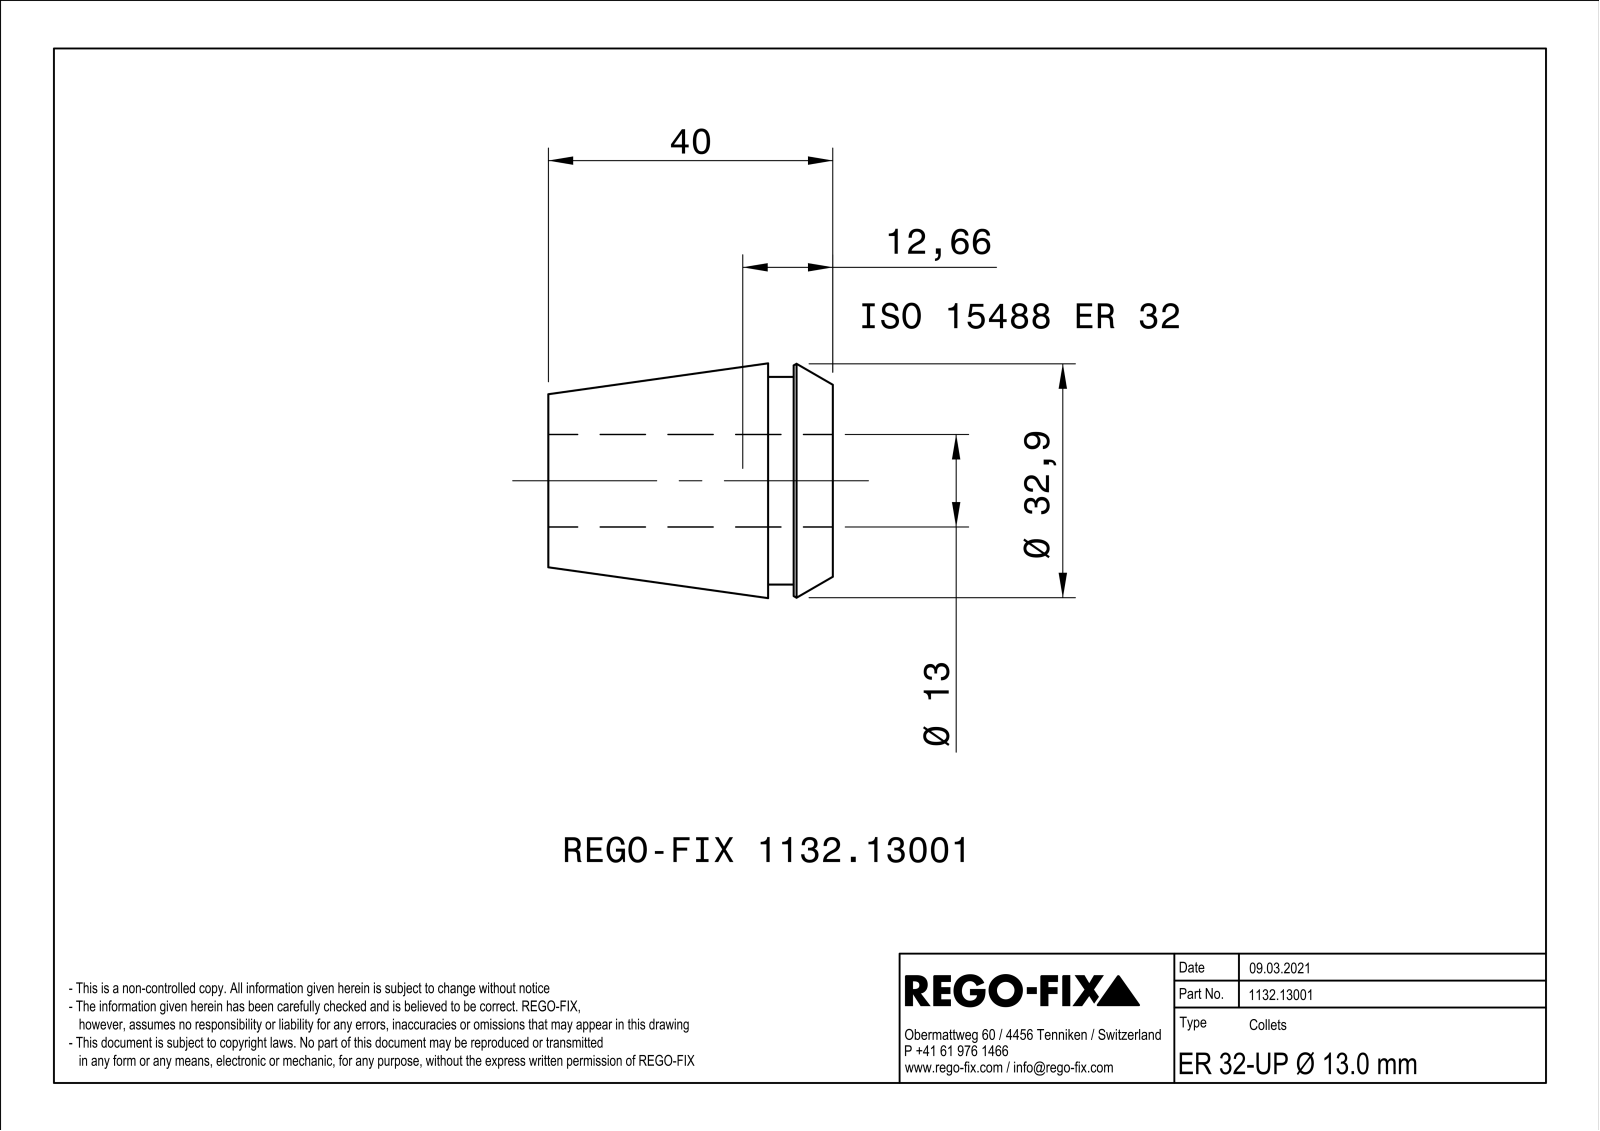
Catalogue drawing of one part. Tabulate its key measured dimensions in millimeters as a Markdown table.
| quantity | value |
| --- | --- |
| part name | NOCUT |
| STEP written by | SIEMENS PLM Software Solid Edge ST10 (AUTOMOTIVE_DESIGN) |
| units | millimeters |
| bodies | 1 solid, 209 faces (88 planar, 41 cylindrical, 80 other) |
| overall size | 40 × 32.98 × 32.98 |
| volume | 16 586 mm³ |
| surface area | 14 338 mm² |
| round holes (diameter × count) | 13 × 1 |
| round bosses / shafts (diameter × count) | 29.2 × 1 |
| partial cylindrical surfaces (radius × count) | 0.4 × 20 |
| main face-to-face distances | 1, 40, 9.1, 30.9, 5.5, 3.6, 34.5, 6, 0.5, 3.1 |
